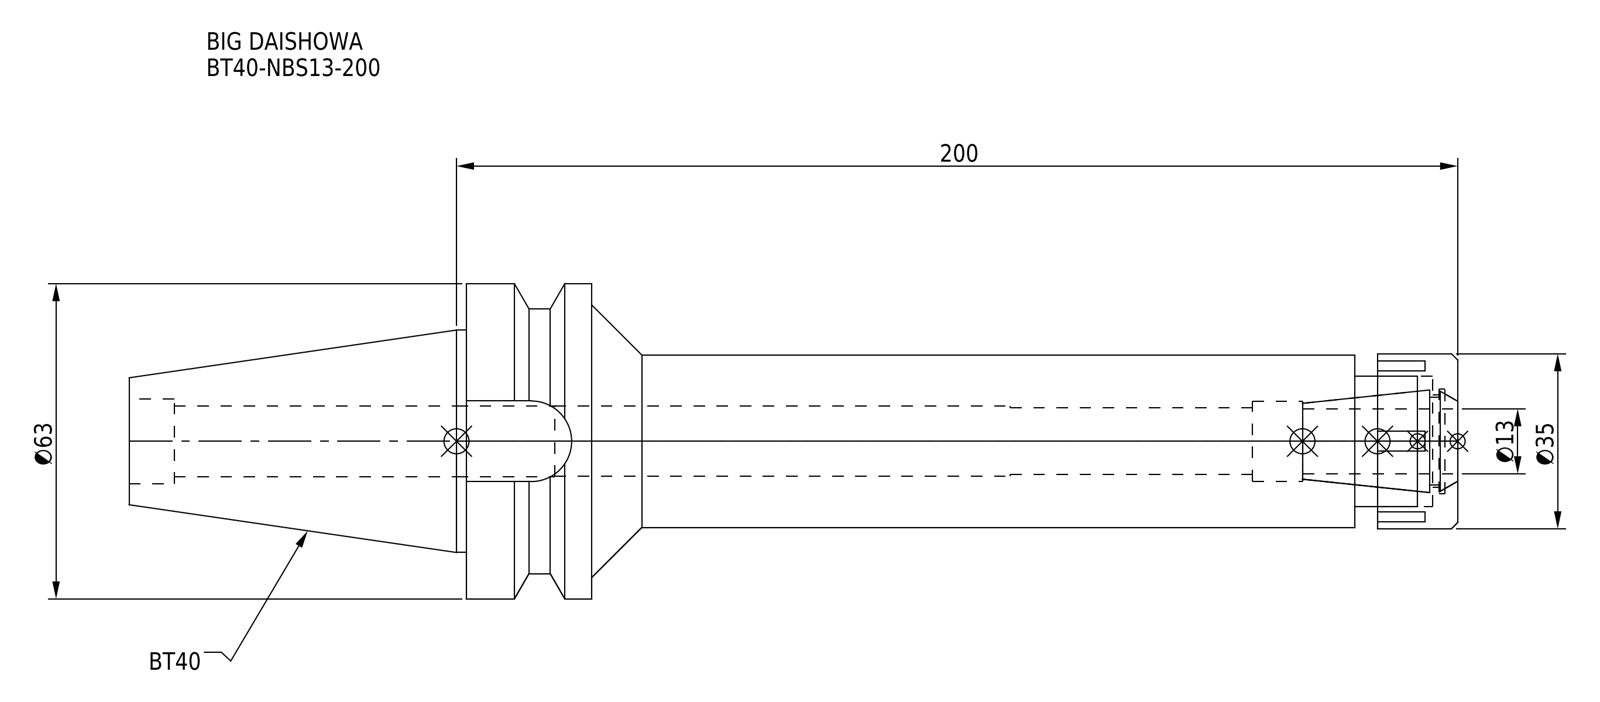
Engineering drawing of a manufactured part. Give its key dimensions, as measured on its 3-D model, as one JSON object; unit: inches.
{"part_name": "BT40-NBS13-200-FreeParts; BT40-NBS13-200.stp; NBN13_1.stp; BT40-NBS13-200_1.stp (+3 more)", "step_written_by": "SolidWorks 2019 (CONFIG_CONTROL_DESIGN)", "units": "inches", "bodies": {"solids": 2, "faces": 93, "planar": 45, "cylindrical": 34, "other": 14}, "overall_size": [10.449, 2.48, 2.48], "volume_in3": 15.56, "surface_area_in2": 80.34, "round_holes": [[0.524, 1], [0.551, 1], [0.559, 1], [0.63, 1], [0.669, 1], [0.728, 1], [0.827, 1], [1.024, 1]], "round_bosses_or_shafts": [[2.48, 1], [2.087, 1], [1.75, 1], [1.378, 1], [1.358, 1]], "partial_cylinders_radius": [[0.317, 1]], "face_to_face_distances": [0.984, 6.811, 7.795, 0.807, 6.181, 0.315, 6.004, 6.988, 0.63, 0.177]}
